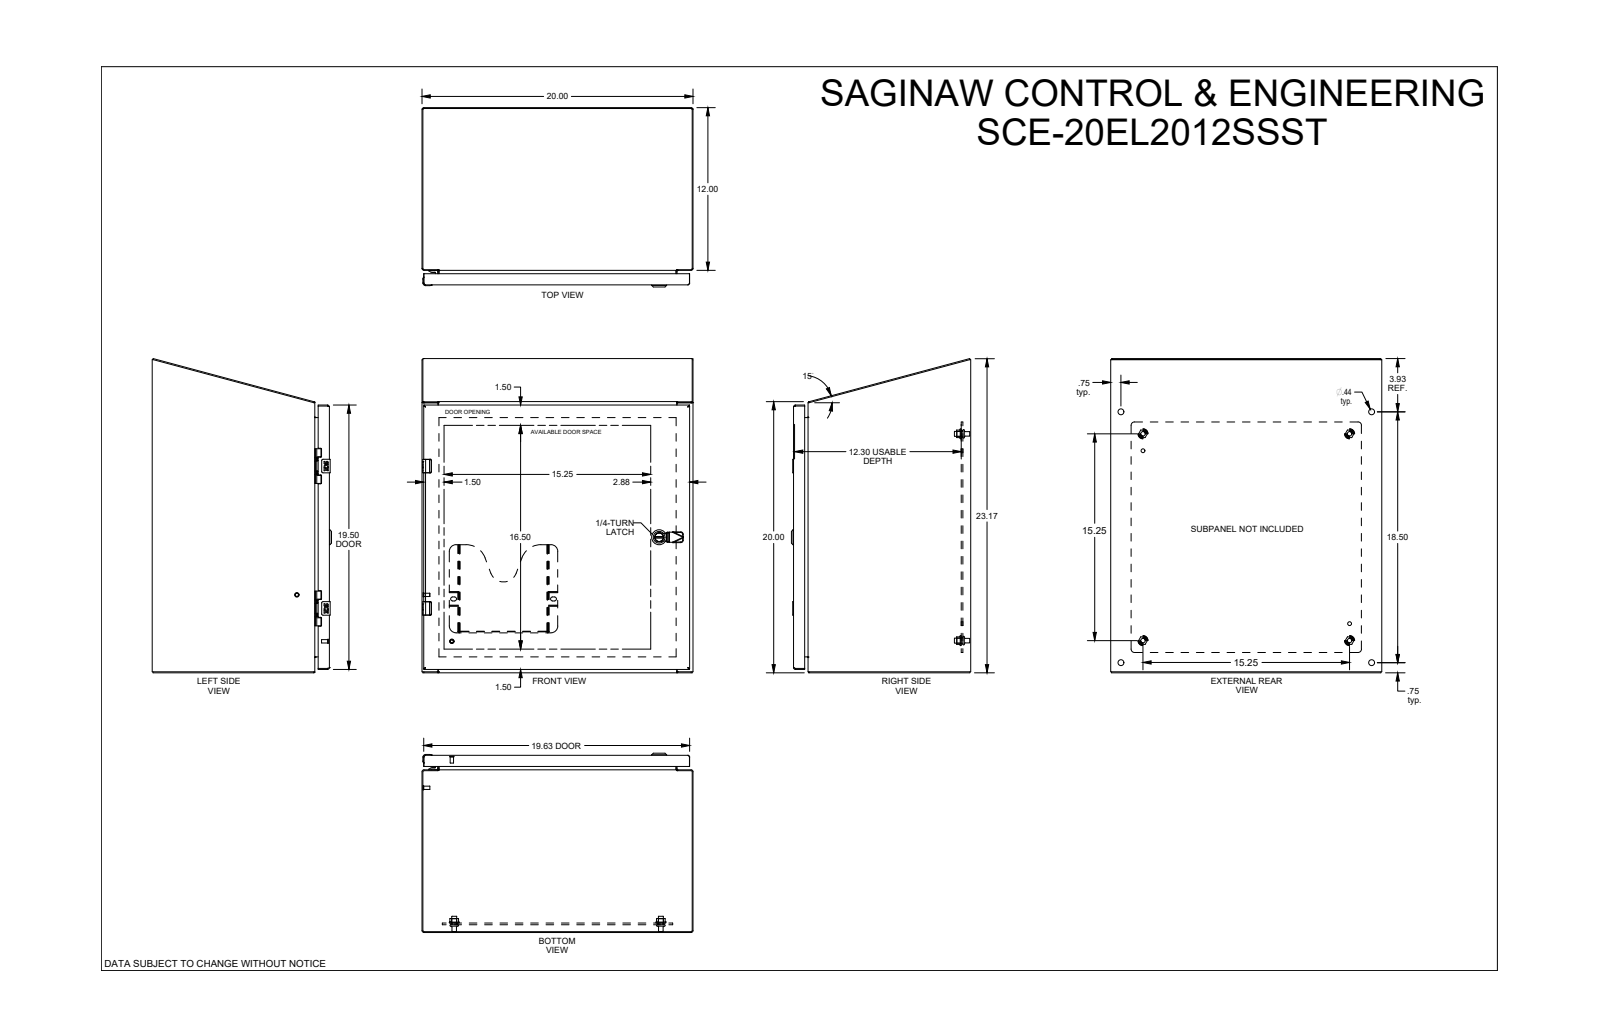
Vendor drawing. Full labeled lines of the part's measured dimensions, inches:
Part name (STEP PRODUCT): SCE-20EL2012SSST_REV1
STEP written by: SolidWorks 2021 (AUTOMOTIVE_DESIGN)
Units: inches
Bodies: 26 solids, 1333 faces (619 planar, 485 cylindrical, 229 other)
Overall size (bounding box): 23.178 × 20 × 13.935
Volume: 200.9 in³ · Surface area: 4 969 in²
Round holes (diameter × count): ⌀0.172 ×4, ⌀0.205 ×4, ⌀0.244 ×4, ⌀0.266 ×4, ⌀0.375 ×4, ⌀0.437 ×4, ⌀0.5 ×4, ⌀0.187 ×2, ⌀0.218 ×2, ⌀0.281 ×2, ⌀0.193 ×1, ⌀0.197 ×1
Round bosses / shafts (diameter × count): ⌀0.375 ×4, ⌀0.33 ×4, ⌀0.25 ×4, ⌀0.248 ×4, ⌀1.102 ×1, ⌀0.78 ×1, ⌀0.63 ×1, ⌀0.504 ×1
Partial cylindrical surfaces — rounded edges, fillets, slot ends (radius × count): R0.015 ×28, R0.04 ×23, R0.22 ×16, R0.06 ×15, R0.07 ×10, R0.145 ×10, R0.03 ×8, R0.031 ×8
Main face-to-face distances: 0.075, 19.925, 0.06, 12.993, 13.068, 13.008, 12.933, 0.575, 0.625, 0.5
Hole centre spacings: 16.953, 10.5, 0.985, 16.927, 17.065, 18.5, 18.986, 23.771
